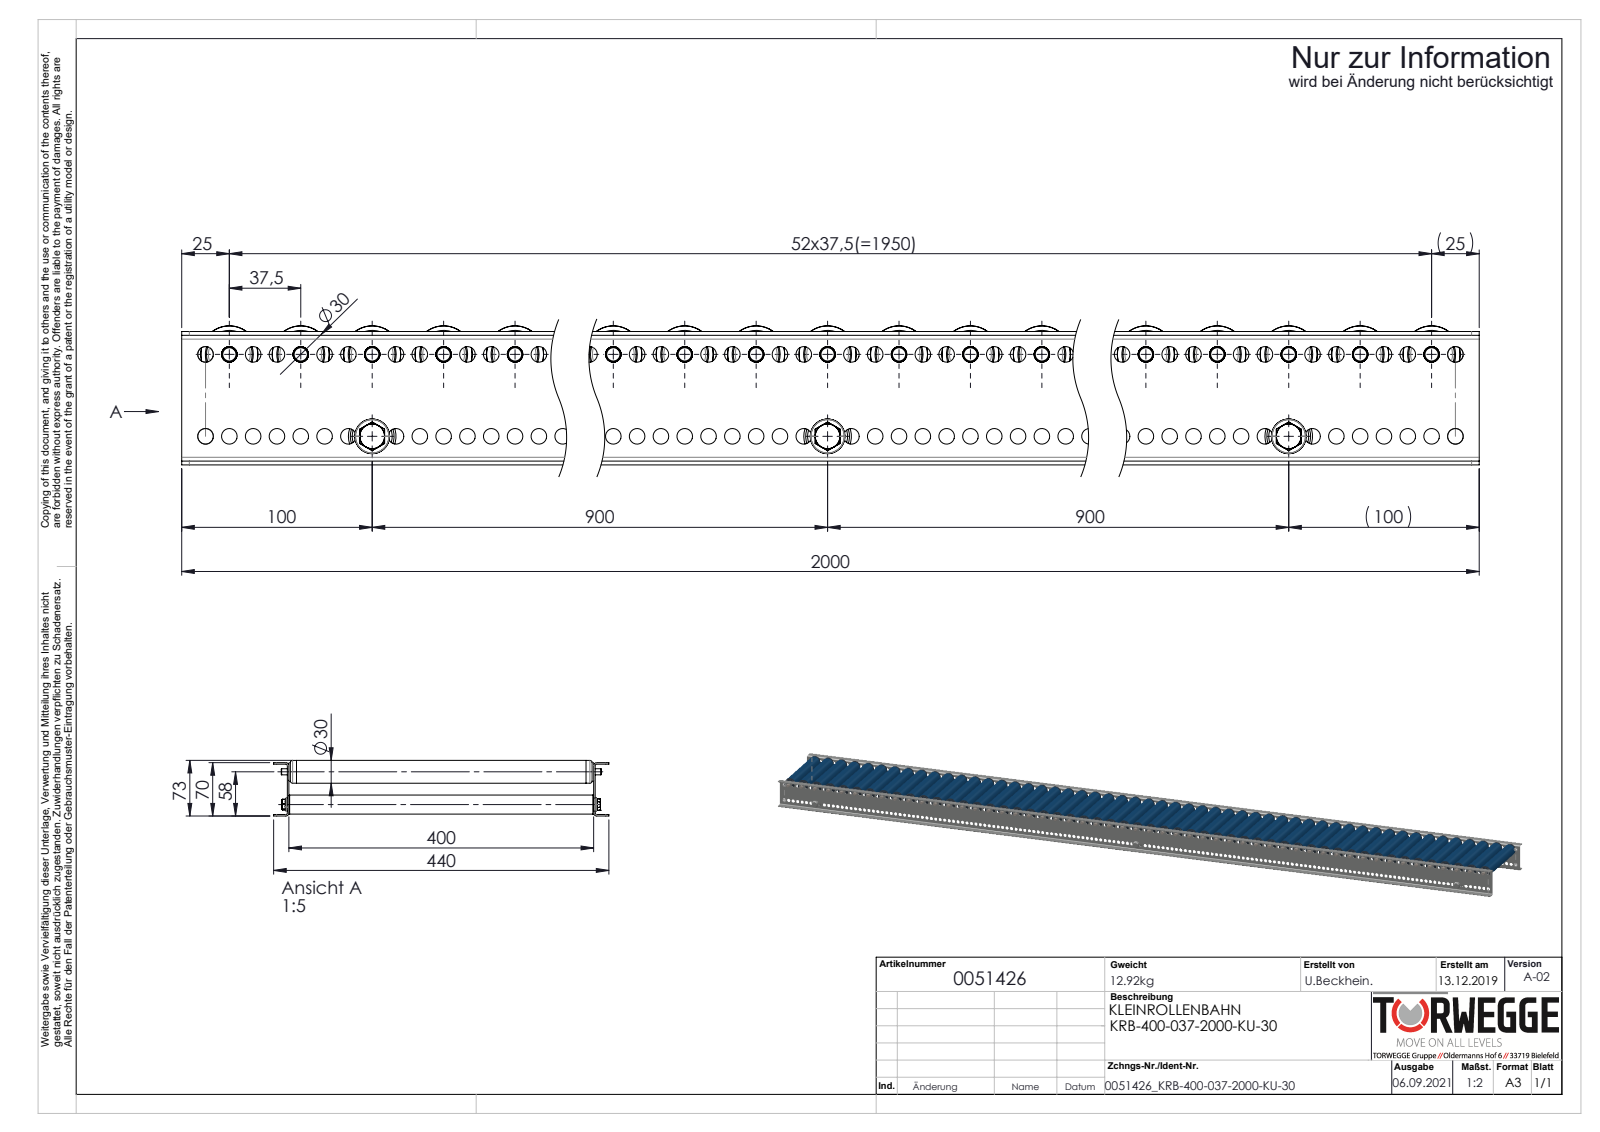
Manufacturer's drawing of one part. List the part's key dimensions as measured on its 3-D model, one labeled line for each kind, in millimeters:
Part name (STEP PRODUCT): 0017013_Tragrollenrohr-Ø30x1,8KU_KFG_L=380; Traversen_KFG_L400; KUT50-30x1,8-KB-A8-FA_KFG_0034506TWG_KUT50-30x1,8-KB-A8-FA-EL=400; S100995_TYP-KUT50-30x1,8-A8 (+4 more)
STEP written by: SolidWorks 2020 (AUTOMOTIVE_DESIGN)
Units: millimetres
Bodies: 123 solids, 12584 faces (3872 planar, 4740 cylindrical, 3972 other)
Overall size (bounding box): 2000 × 440 × 73
Volume: 5 305 000 mm³ · Surface area: 5 769 000 mm²
Round holes (diameter × count): ⌀8.2 ×318, ⌀8.1 ×53, ⌀22.6 ×53, ⌀25.2 ×53, ⌀6.8 ×3, ⌀21 ×3
Round bosses / shafts (diameter × count): ⌀8 ×56, ⌀30 ×53, ⌀29.9 ×53, ⌀26.5 ×53, ⌀26.4 ×53, ⌀24 ×53, ⌀25 ×3
Partial cylindrical surfaces — rounded edges, fillets, slot ends (radius × count): R5.05 ×53, R4 ×8, R2 ×4
Main face-to-face distances: 2, 402, 400, 68, 404, 70, 66, 10, 390, 12
Hole centre spacings: 12.5, 25, 37.5, 50, 62.5, 75, 87.5, 100
